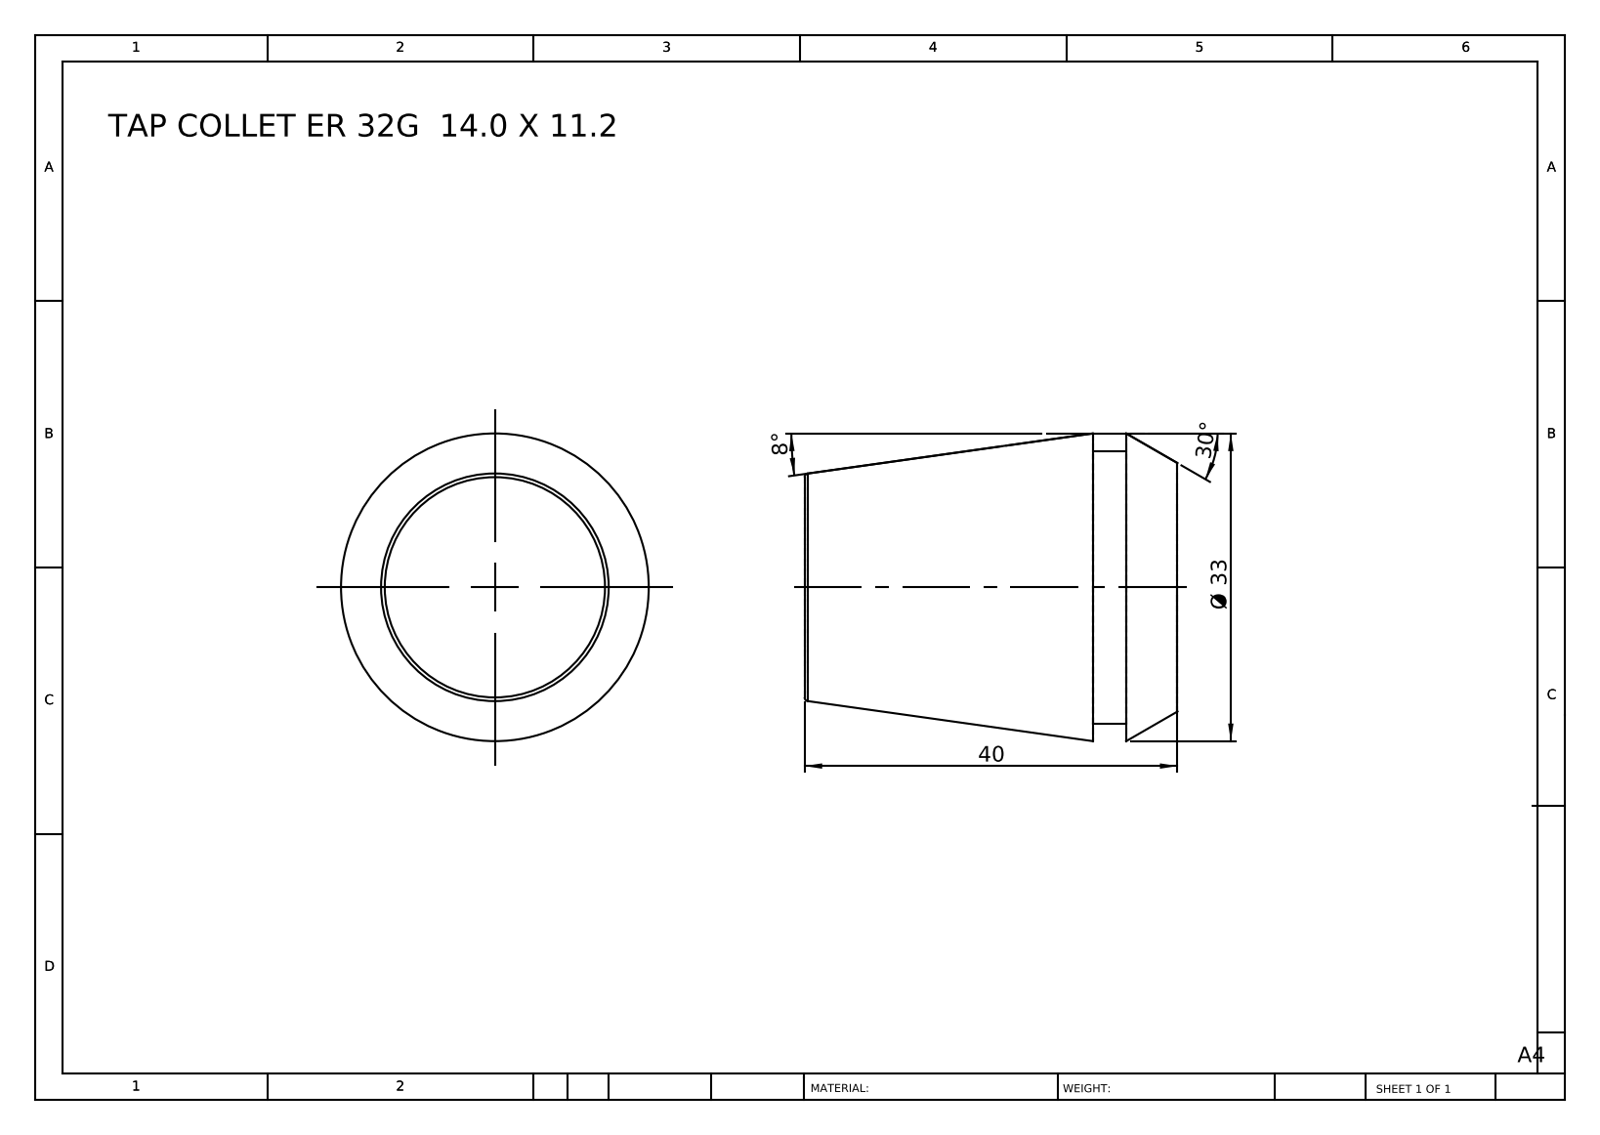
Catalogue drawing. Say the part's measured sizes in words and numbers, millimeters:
The part is named "TAP COLLET ER 32G 14.0 X 11.2". Its 3-D file was written by "SolidWorks 2014 (CONFIG_CONTROL_DESIGN)". It is 1 solid with 12 faces: 4 planar, 2 cylindrical and 6 other. Overall it measures 40 by 33 by 33 millimeters. Its volume is 26 350 cubic millimeters and its surface area 5 119 square millimeters. Round bosses or shafts: 1 of diameter 29.2. The main face-to-face distances are 40, 9.1, 30.9, 5.5, 3.6, 34.5.
